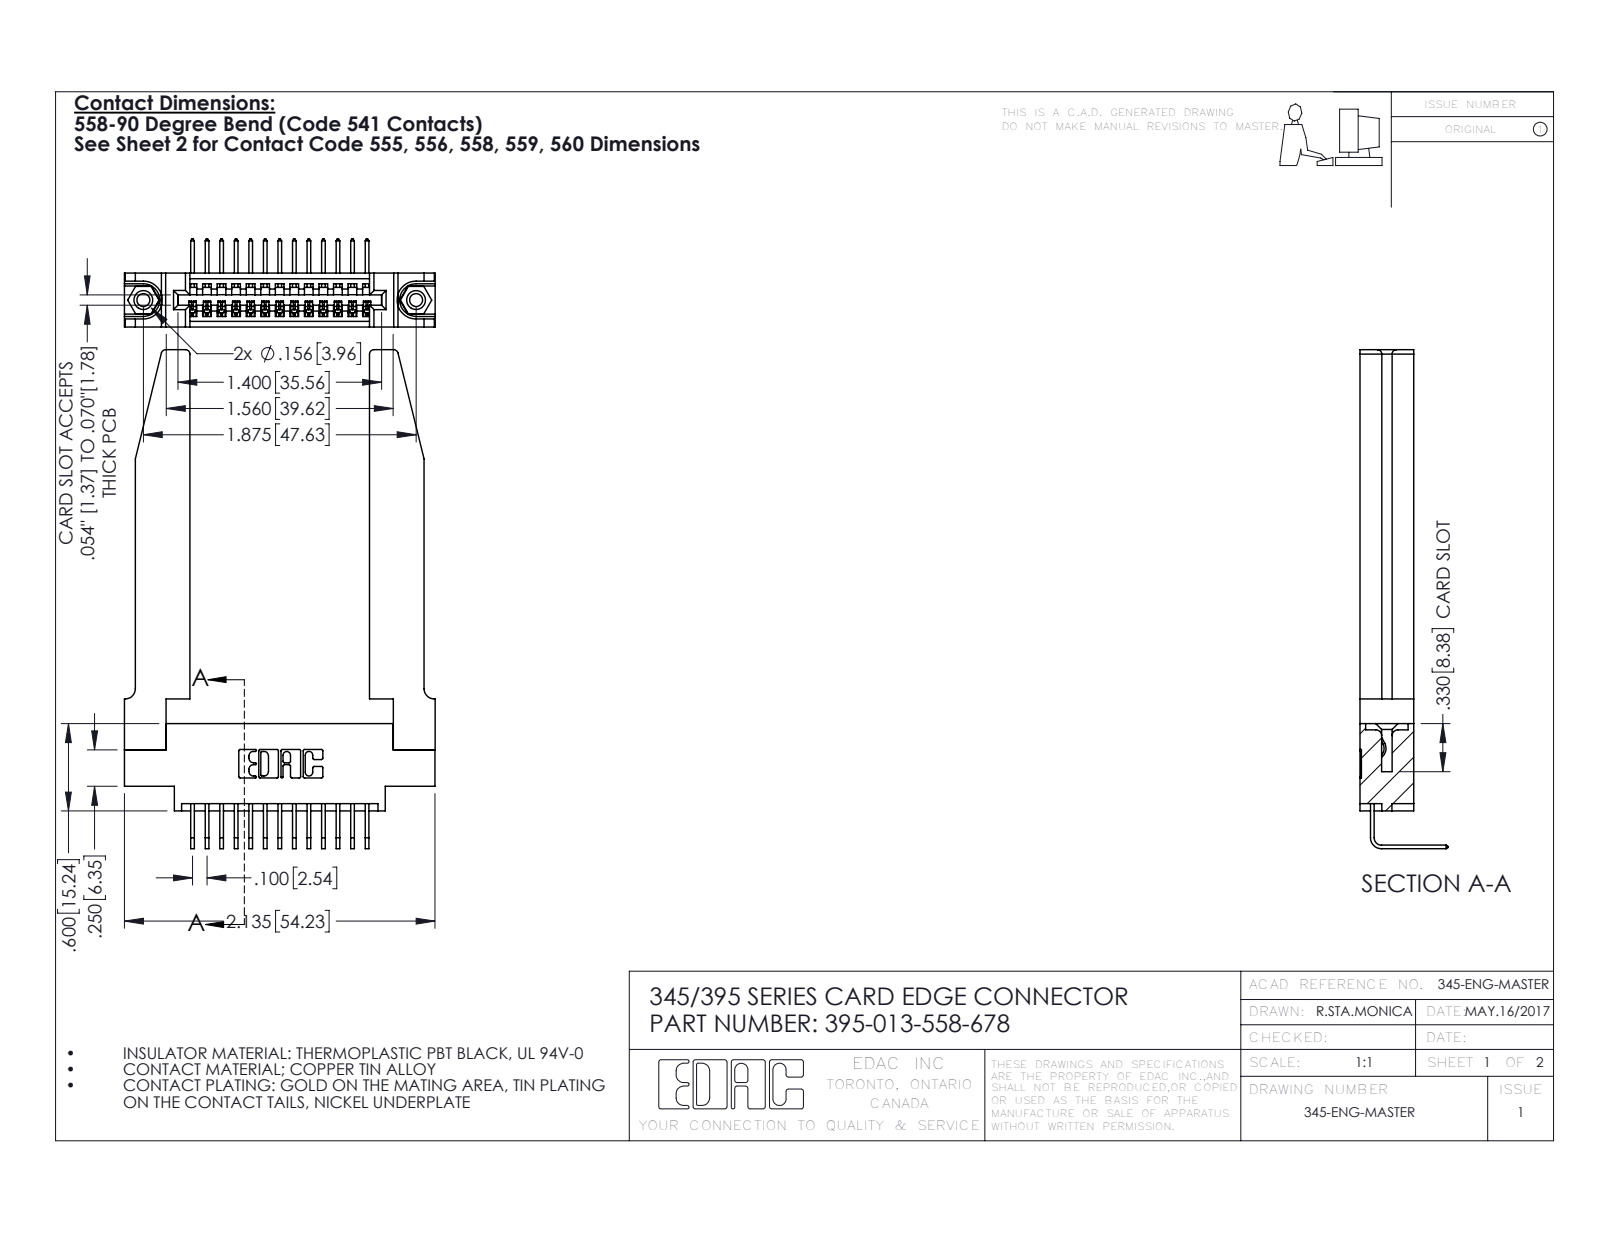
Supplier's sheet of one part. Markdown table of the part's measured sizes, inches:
| quantity | value |
| --- | --- |
| part name | 345 Part_0.170 Offset - 0.156 Dia-TH; 345-292-001_558 Tail - 2; 345-250-001_345-250-001-102; 345-220-078_345-220-078 (+1 more) |
| STEP written by | SolidWorks 2016 (CONFIG_CONTROL_DESIGN) |
| units | inches |
| bodies | 18 solids, 1144 faces (772 planar, 320 cylindrical, 52 other) |
| overall size | 3.429 × 2.136 × 0.605 |
| volume | 0.77 in³ |
| surface area | 20.57 in² |
| round holes (diameter × count) | 0.089 × 2, 0.125 × 2, 0.156 × 2, 0.064 × 1 |
| round bosses / shafts (diameter × count) | 0.155 × 2 |
| partial cylindrical surfaces (radius × count) | 0.006 × 26, 0.01 × 22, 0.03 × 8, 0.007 × 6, 0.031 × 6, 0.026 × 3, 0.031 × 2, 0.04 × 2 |
| main face-to-face distances | 0.37, 0.072, 0.298, 0.148, 0.15, 0.22, 0.077, 1.235, 0.098, 0.272 |
| hole center spacings | 0.27, 1.643, 1.875 |
